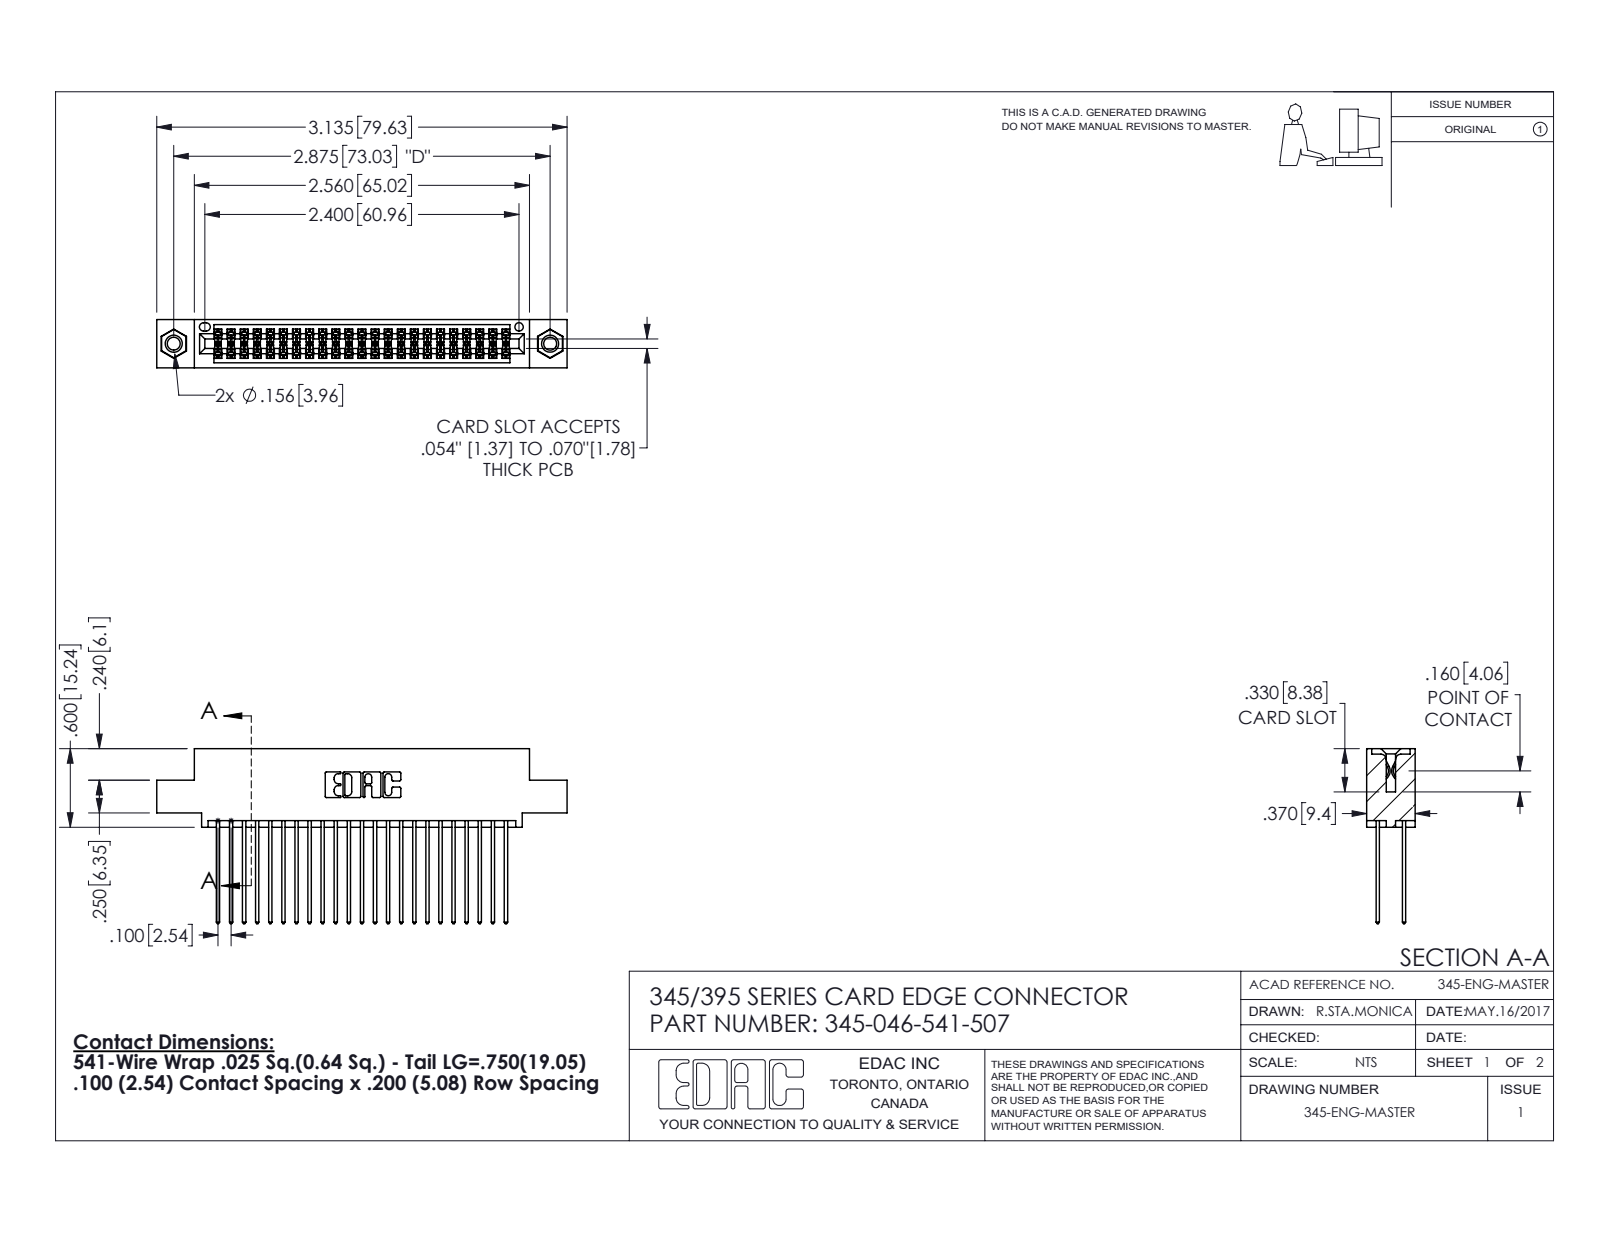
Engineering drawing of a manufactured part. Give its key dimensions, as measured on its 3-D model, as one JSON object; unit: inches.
{"part_name": "345-046-541-507; 345 Part_0.110 Offset - 0.156 Dia-TI; 345-292-001_345-293-141; 345-250-001_345-250-005-103", "step_written_by": "SolidWorks 2016 (CONFIG_CONTROL_DESIGN)", "units": "inches", "bodies": {"solids": 49, "faces": 2490, "planar": 1634, "cylindrical": 840, "other": 16}, "overall_size": [3.135, 1.337, 0.37], "volume_in3": 0.472, "surface_area_in2": 19.26, "round_holes": [[0.098, 2], [0.125, 2], [0.156, 2], [0.064, 1]], "round_bosses_or_shafts": [[0.155, 2]], "partial_cylinders_radius": [[0.006, 69], [0.01, 46], [0.01, 22], [0.007, 6], [0.031, 6], [0.026, 3], [0.014, 2], [0.019, 2]], "face_to_face_distances": [0.072, 0.298, 0.2, 0.098, 0.272, 0.025, 0.37, 0.225, 0.175, 0.149], "hole_center_spacings": [0.27, 2.641, 2.875]}
